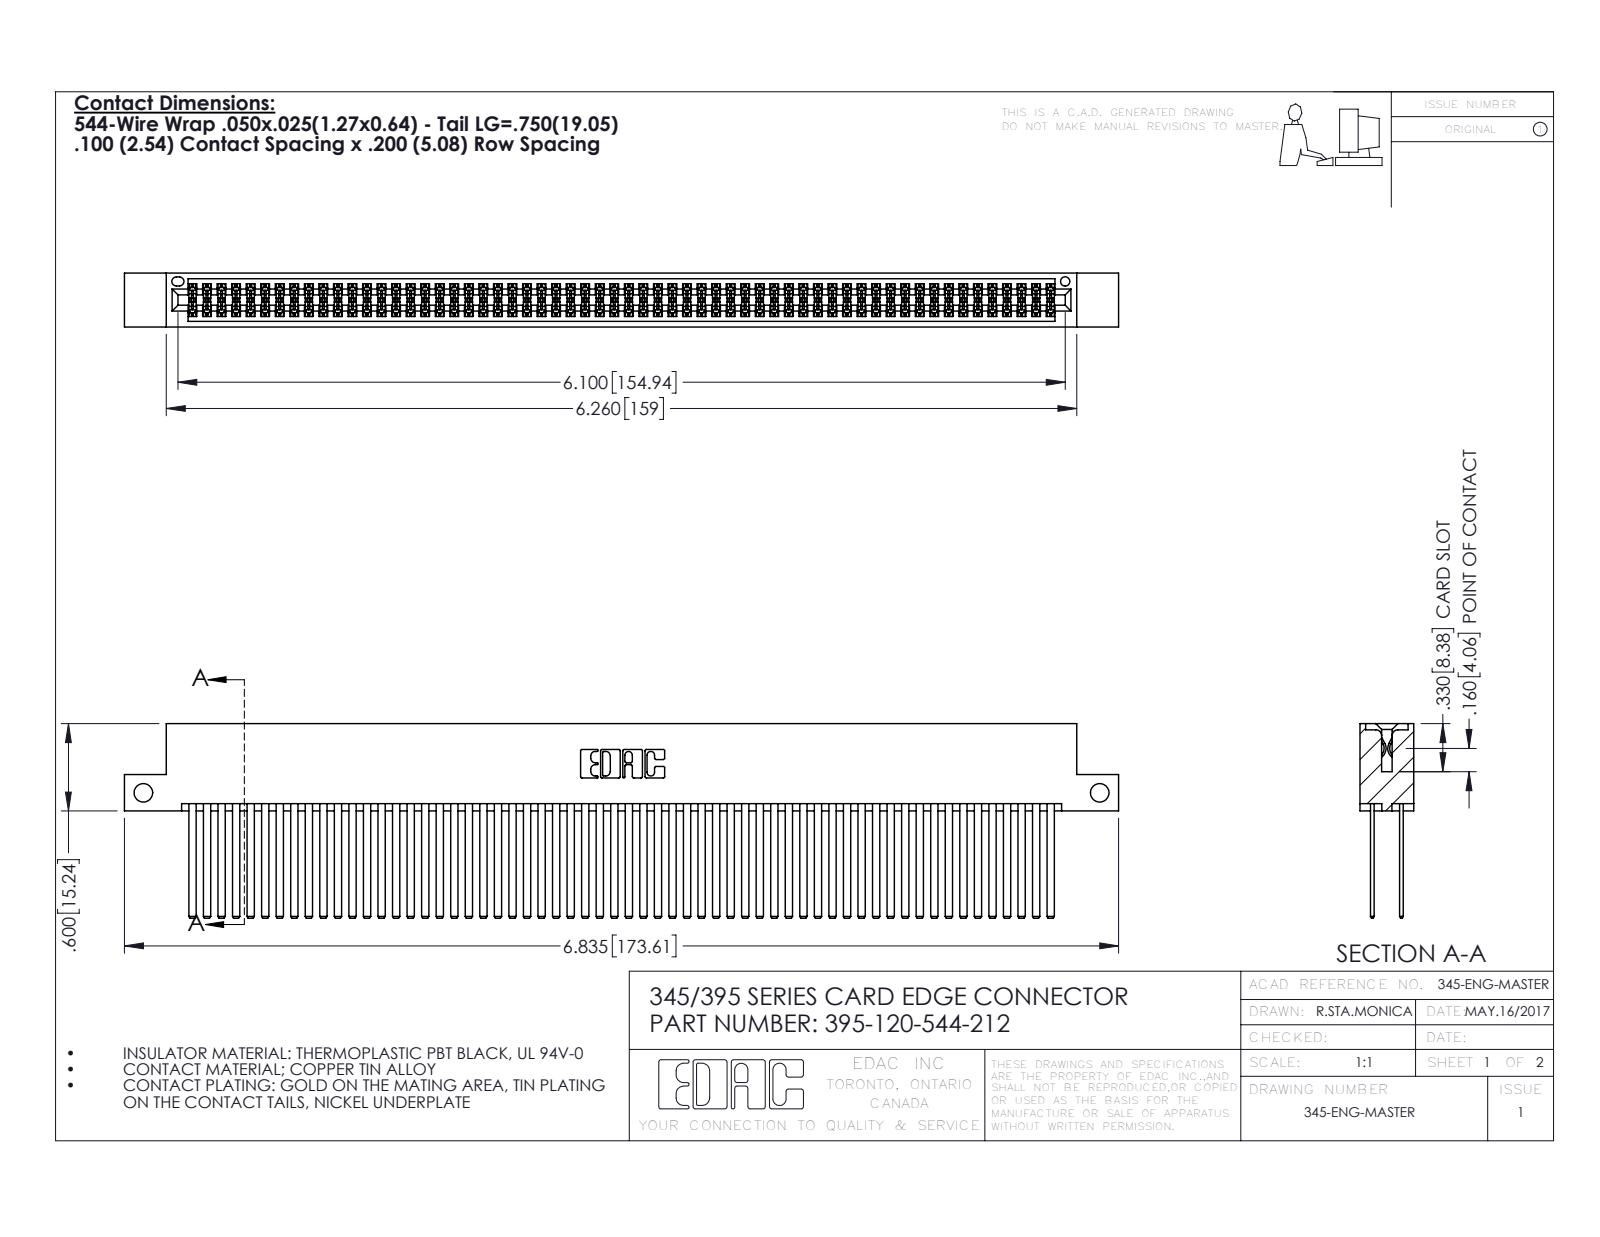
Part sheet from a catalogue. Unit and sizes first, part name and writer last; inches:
Units: inches
Overall size (bounding box): 6.835 × 1.337 × 0.37
Round holes (diameter × count): ⌀0.128 ×2, ⌀0.064 ×1
Partial cylindrical surfaces — rounded edges, fillets, slot ends (radius × count): R0.006 ×180, R0.01 ×22, R0.007 ×6, R0.031 ×6, R0.026 ×3, R0.014 ×2, R0.019 ×2, R0.022 ×2
Main face-to-face distances: 0.2, 0.025, 0.298, 0.072, 0.098, 0.272, 0.225, 0.175, 0.37, 0.05
Hole centre spacings: 6.575
Volume: 1.137 in³ · Surface area: 50.65 in²
Bodies: 121 solids, 5406 faces (3560 planar, 1846 cylindrical, 0 other)
Part name (STEP PRODUCT): 395-120-544-212; 345-292-001_345-293-144; 345 Part_Flush Mounting Lugs - Side Mount
STEP written by: SolidWorks 2016 (CONFIG_CONTROL_DESIGN)
